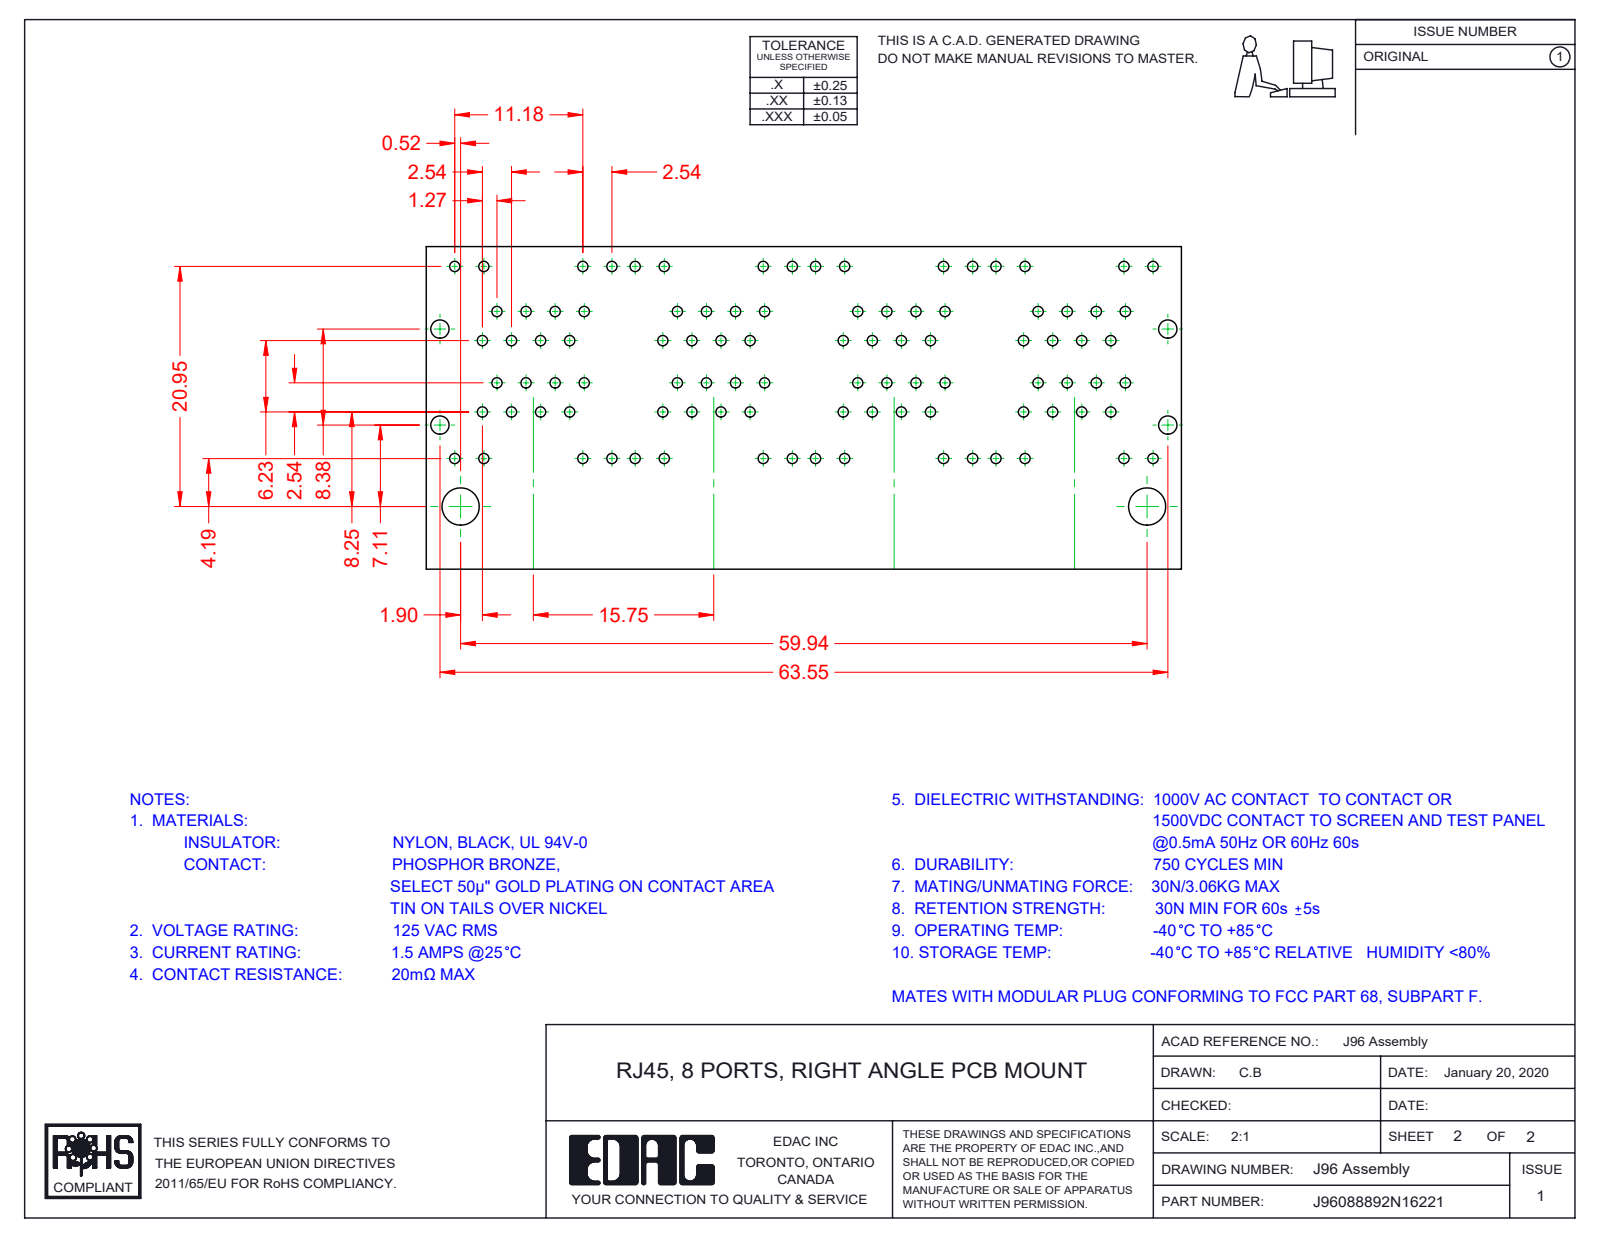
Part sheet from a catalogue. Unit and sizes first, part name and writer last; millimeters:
Units: millimetres
Overall size (bounding box): 67.35 × 31.38 × 28.68
Round holes (diameter × count): ⌀1.7 ×3
Round bosses / shafts (diameter × count): ⌀1.68 ×3
Partial cylindrical surfaces — rounded edges, fillets, slot ends (radius × count): R0.25 ×124, R0.35 ×73, R1 ×72, R0.5 ×49, R0.91 ×32, R0.2 ×27, R0.27 ×14, R0.7 ×11
Main face-to-face distances: 15.75, 0.35, 9.95, 1.17, 1.6, 0.54, 9.98, 10.18, 12.67, 3.37
Hole centre spacings: 15.75, 31.5
Volume: 24 149 mm³ · Surface area: 63 596 mm²
Bodies: 96 solids, 7820 faces (6105 planar, 1404 cylindrical, 311 other)
Part name (STEP PRODUCT): 96 LED RH Upper_6-Red-Green; 96 Insulator_8 Ports; 96 Insulator Insert; 96 LED LH Lower_1-Yellow (+8 more)
STEP written by: SolidWorks 2016 (CONFIG_CONTROL_DESIGN)
